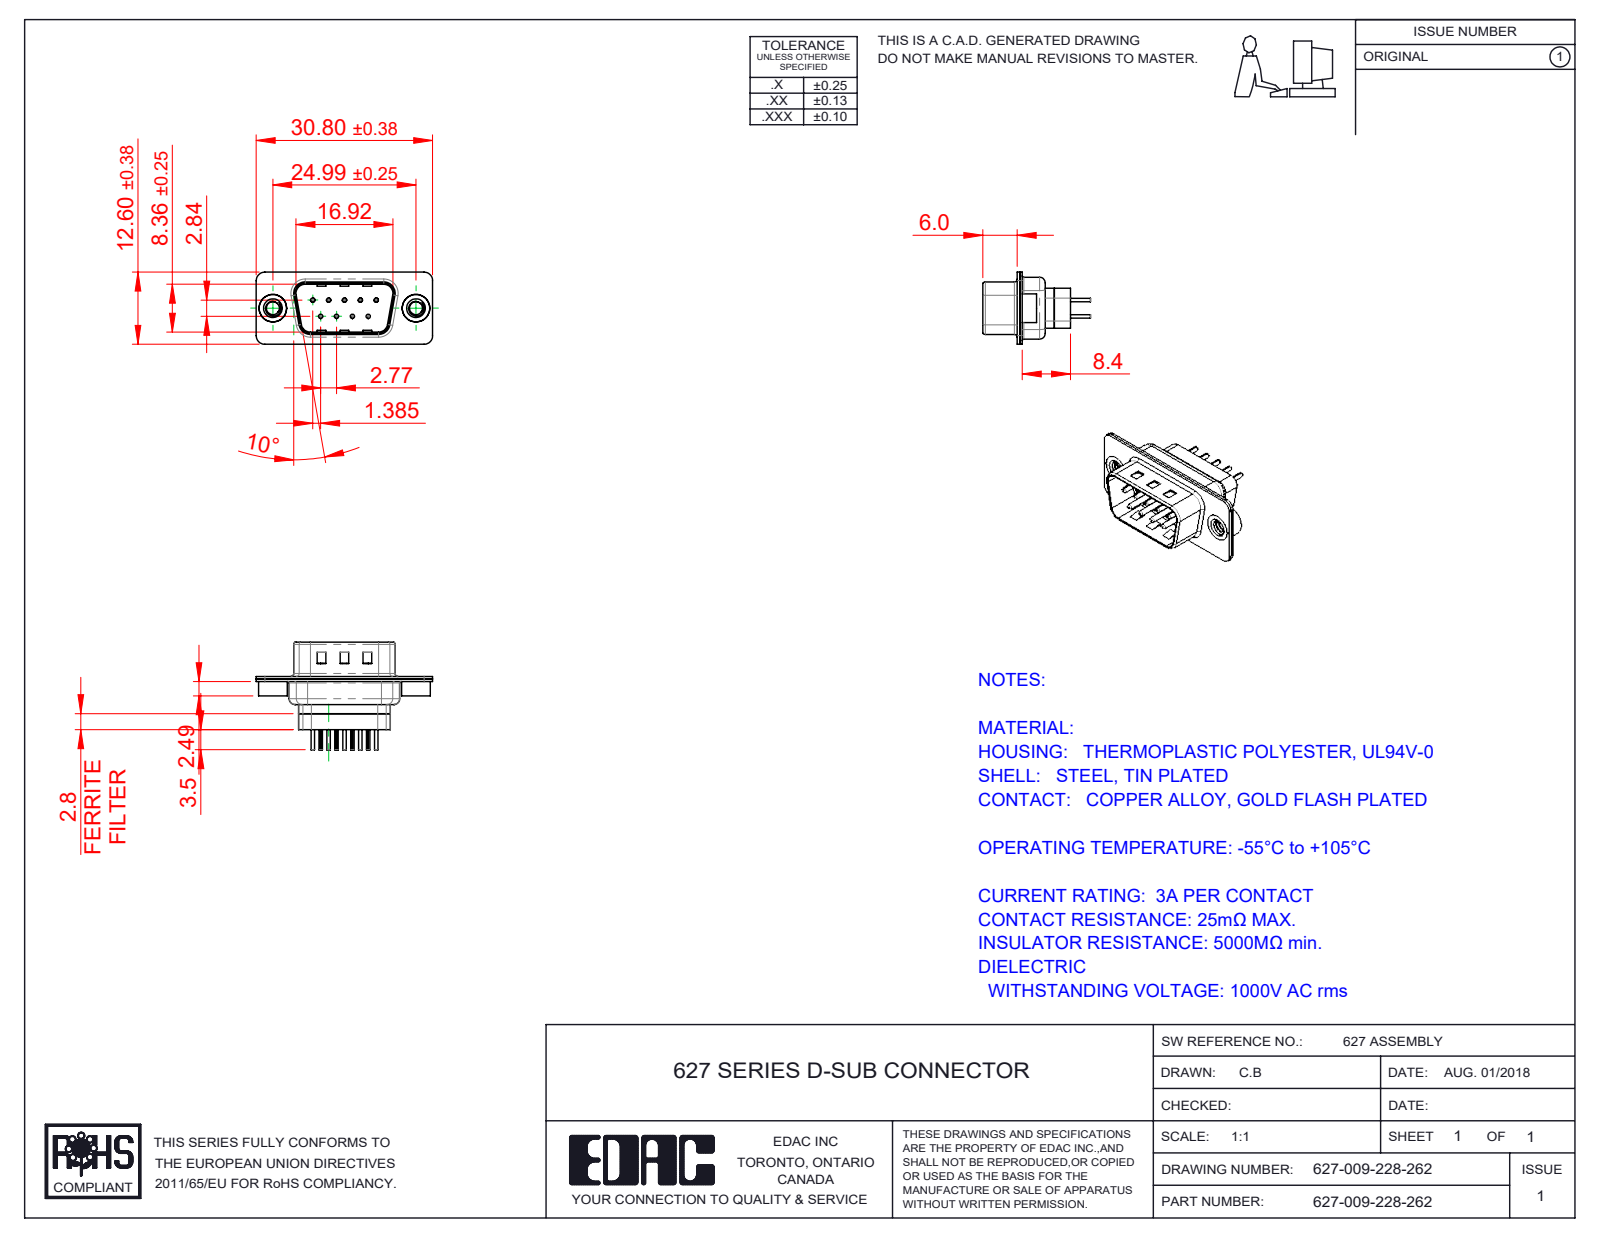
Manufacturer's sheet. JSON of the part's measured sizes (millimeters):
{"part_name": "627 Contact Row 2_28L; 627 Contact Row 1_28L; 627 Housing_09 FF; 627 4-40 Threaded Rivet (+3 more)", "step_written_by": "SolidWorks 2020 (CONFIG_CONTROL_DESIGN)", "units": "millimeters", "bodies": {"solids": 15, "faces": 1211, "planar": 329, "cylindrical": 483, "other": 399}, "overall_size": [30.8, 18.8, 12.6], "volume_mm3": 1555, "surface_area_mm2": 4382, "round_holes": [[0.2, 9], [0.35, 9], [1.1, 9], [1.6, 9], [2.26, 2], [4, 2], [4.8, 2]], "round_bosses_or_shafts": [[2, 9], [1.5, 9], [0.75, 9], [0.6, 9], [5, 2], [4.9, 2]], "partial_cylinders_radius": [[0.1, 18], [1.5, 18], [2, 12], [0.5, 8], [1.6, 8], [0.25, 4], [0.6, 4], [0.65, 4]], "face_to_face_distances": [0.45, 0.4, 0.9, 6.5, 6.05, 5.6, 0.82, 9.58, 8.4, 1.4], "hole_center_spacings": [3.16, 2.77, 5.54, 5.03, 5.04, 8.31, 7.48, 7.49]}
